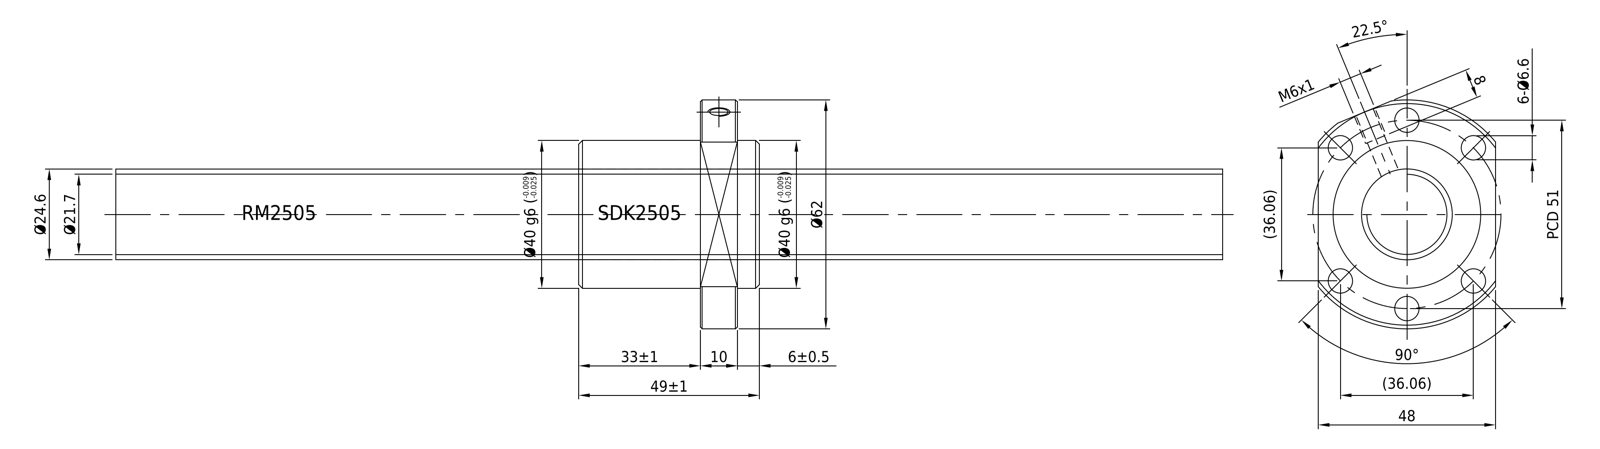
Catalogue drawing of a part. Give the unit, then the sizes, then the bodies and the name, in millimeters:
Units: millimetres
Overall size (bounding box): 300 × 62 × 48
Round holes (diameter × count): ⌀6.6 ×6, ⌀3 ×1, ⌀5 ×1, ⌀25 ×1
Round bosses / shafts (diameter × count): ⌀40 ×1, ⌀24.6 ×1
Partial cylindrical surfaces — rounded edges, fillets, slot ends (radius × count): R31 ×1
Main face-to-face distances: 10, 125.5, 174.5, 43, 33, 6, 16, 49, 131.5, 141.5
Hole centre spacings: 25.5, 19.52, 36.06, 47.12, 51
Volume: 191 311 mm³ · Surface area: 39 842 mm²
Bodies: 2 solids, 48 faces (9 planar, 27 cylindrical, 12 other)
Part name (STEP PRODUCT): SDK2505; RM2505
STEP written by: SolidWorks 2013 (CONFIG_CONTROL_DESIGN)
